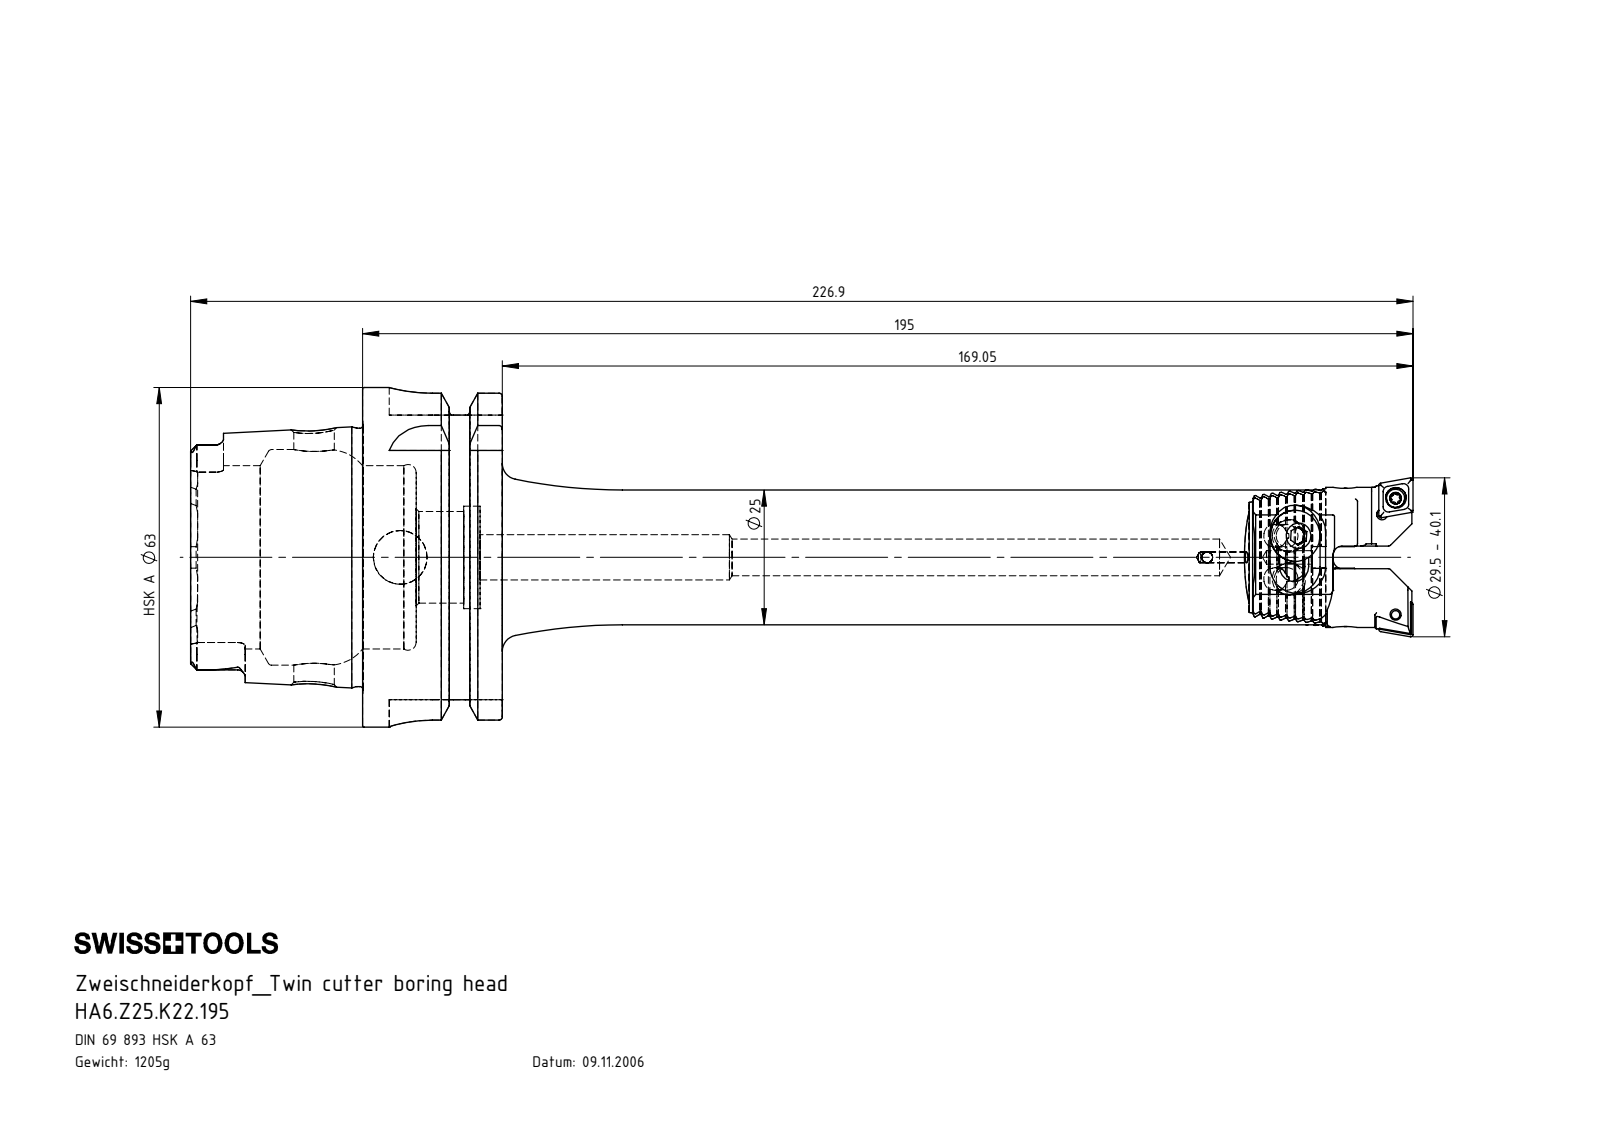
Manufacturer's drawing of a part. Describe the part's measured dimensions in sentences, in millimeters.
The part is named "HA6.Z25.K22.195; Z25-ER1.001.012; CCMT060204; WCA-ER2.001.006_B (+7 more)". Its 3-D file was written by "SolidWorks 2022 (CONFIG_CONTROL_DESIGN)". It is 14 solids with 1092 faces: 502 planar, 281 cylindrical and 309 other. Overall it measures 226.9 by 63 by 63 millimeters. Its volume is 154 075 cubic millimeters and its surface area 43 573 square millimeters. Round holes: 5 of diameter 2, 2 of diameter 1.6, 2 of diameter 2.05, 2 of diameter 2.8, 2 of diameter 3.85, 2 of diameter 4.2, 2 of diameter 5.3, 2 of diameter 6, 1 of diameter 2.5, 1 of diameter 3.5, 1 of diameter 6.8, 1 of diameter 7.5. Round bosses or shafts: 2 of diameter 9.5, 2 of diameter 9.2, 2 of diameter 5, 2 of diameter 3.4, 2 of diameter 2.5, 1 of diameter 63, 1 of diameter 54.95, 1 of diameter 47.94. Partial cylindrical surfaces (rounded edges, fillets, slot ends): 18 of radius 0.12, 18 of radius 0.5, 16 of radius 0.12, 12 of radius 0.21, 10 of radius 0.36, 6 of radius 1.4, 4 of radius 2, 4 of radius 2.8. The main face-to-face distances are 25.95, 1.43, 16, 9.95, 2.86, 1.39, 5.71, 31.9, 41.85, 57.85. The hole center spacings are 3.9, 4, 7, 18.02, 18.11, 20.91, 193.28, 13.52.
